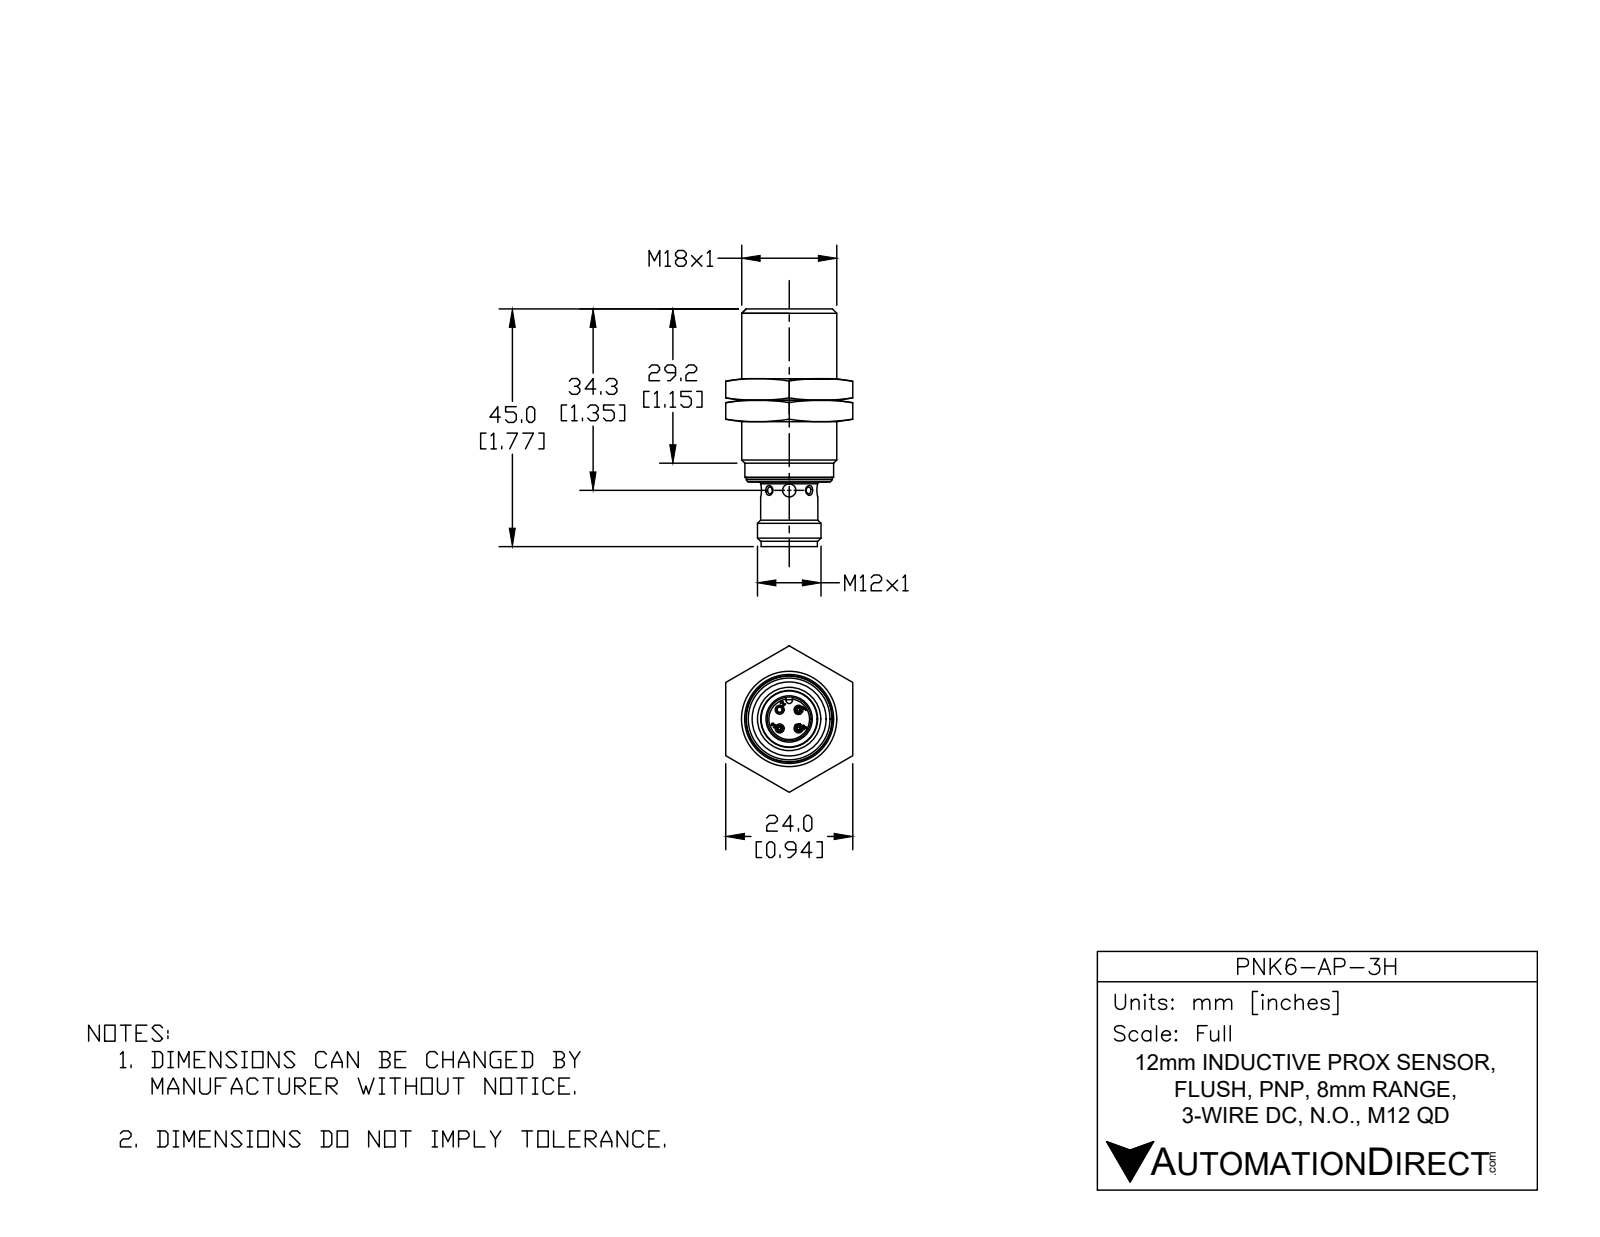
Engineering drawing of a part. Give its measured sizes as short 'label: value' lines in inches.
name: PNK6-AP-3H
written by: SolidWorks 2017 (AUTOMOTIVE_DESIGN)
unit: in
bodies: 1 solid, 476 faces (118 planar, 129 cylindrical, 229 other)
size: 1.772 × 0.709 × 0.709
volume: 0.401 in³; area: 7.642 in²
holes: 3× ⌀0.04, 3× ⌀0.043, 2× ⌀0.098, 1× ⌀0.038, 1× ⌀0.323, 1× ⌀0.327, 1× ⌀0.394, 1× ⌀0.618
bosses: 9× ⌀0.039, 1× ⌀0.709, 1× ⌀0.661, 1× ⌀0.642, 1× ⌀0.638, 1× ⌀0.616, 1× ⌀0.472, 1× ⌀0.425
rounds: 24× R0.004, 6× R0.039, 6× R0.071, 1× R0.024, 1× R0.031
face distances: 0.452, 0.03, 0.422, 1.236, 1.207, 0.785, 1.291, 0.055, 1.262, 0.84
hole spacings: 0.098, 0.139, 0.197
